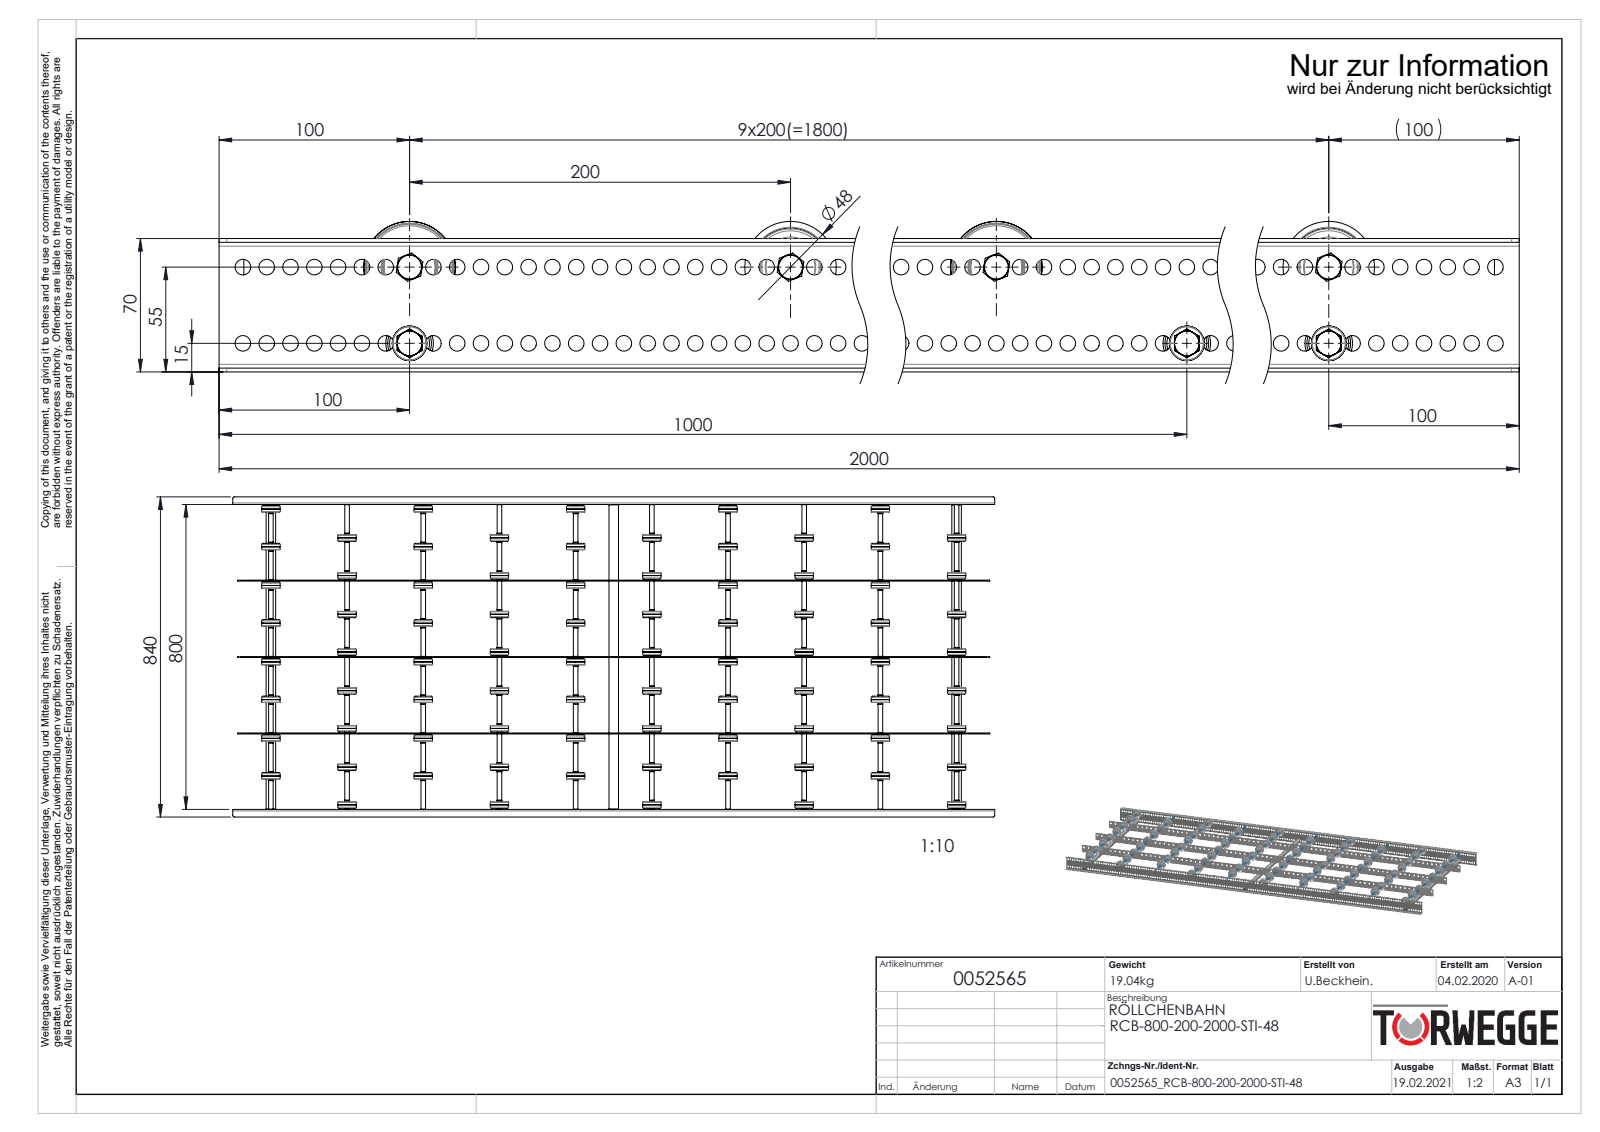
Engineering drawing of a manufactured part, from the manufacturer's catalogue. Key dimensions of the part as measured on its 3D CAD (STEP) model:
Part name (STEP PRODUCT): 0046278_KB-ROHR-12X1,75mm_KFG_L75; Traversen_KFG_L800; S106837_Gewindestange-M8-KFG_L820; Hutmutter_DIN_1587_M8 (+6 more)
STEP written by: SolidWorks 2020 (AUTOMOTIVE_DESIGN)
Units: millimetres
Bodies: 290 solids, 9690 faces (1800 planar, 4334 cylindrical, 3556 other)
Overall size (bounding box): 2000 × 840 × 79
Volume: 4 082 000 mm³ · Surface area: 3 310 000 mm²
Round holes (diameter × count): ⌀8.2 ×318, ⌀8.5 ×79, ⌀6.65 ×10, ⌀8 ×10, ⌀9.65 ×10, ⌀15 ×10, ⌀41 ×10, ⌀6.8 ×3, ⌀21 ×3
Round bosses / shafts (diameter × count): ⌀48 ×10, ⌀13 ×10, ⌀12.5 ×10, ⌀12.4 ×10, ⌀12 ×10, ⌀11.5 ×10, ⌀25 ×3, ⌀8 ×3
Partial cylindrical surfaces — rounded edges, fillets, slot ends (radius × count): R4 ×8, R2 ×4, R5 ×4
Main face-to-face distances: 200.5, 401, 2, 203, 2.5, 198, 802, 601.5, 403.5, 398.5
Hole centre spacings: 12.5, 25, 37.5, 50, 62.5, 75, 87.5, 100
